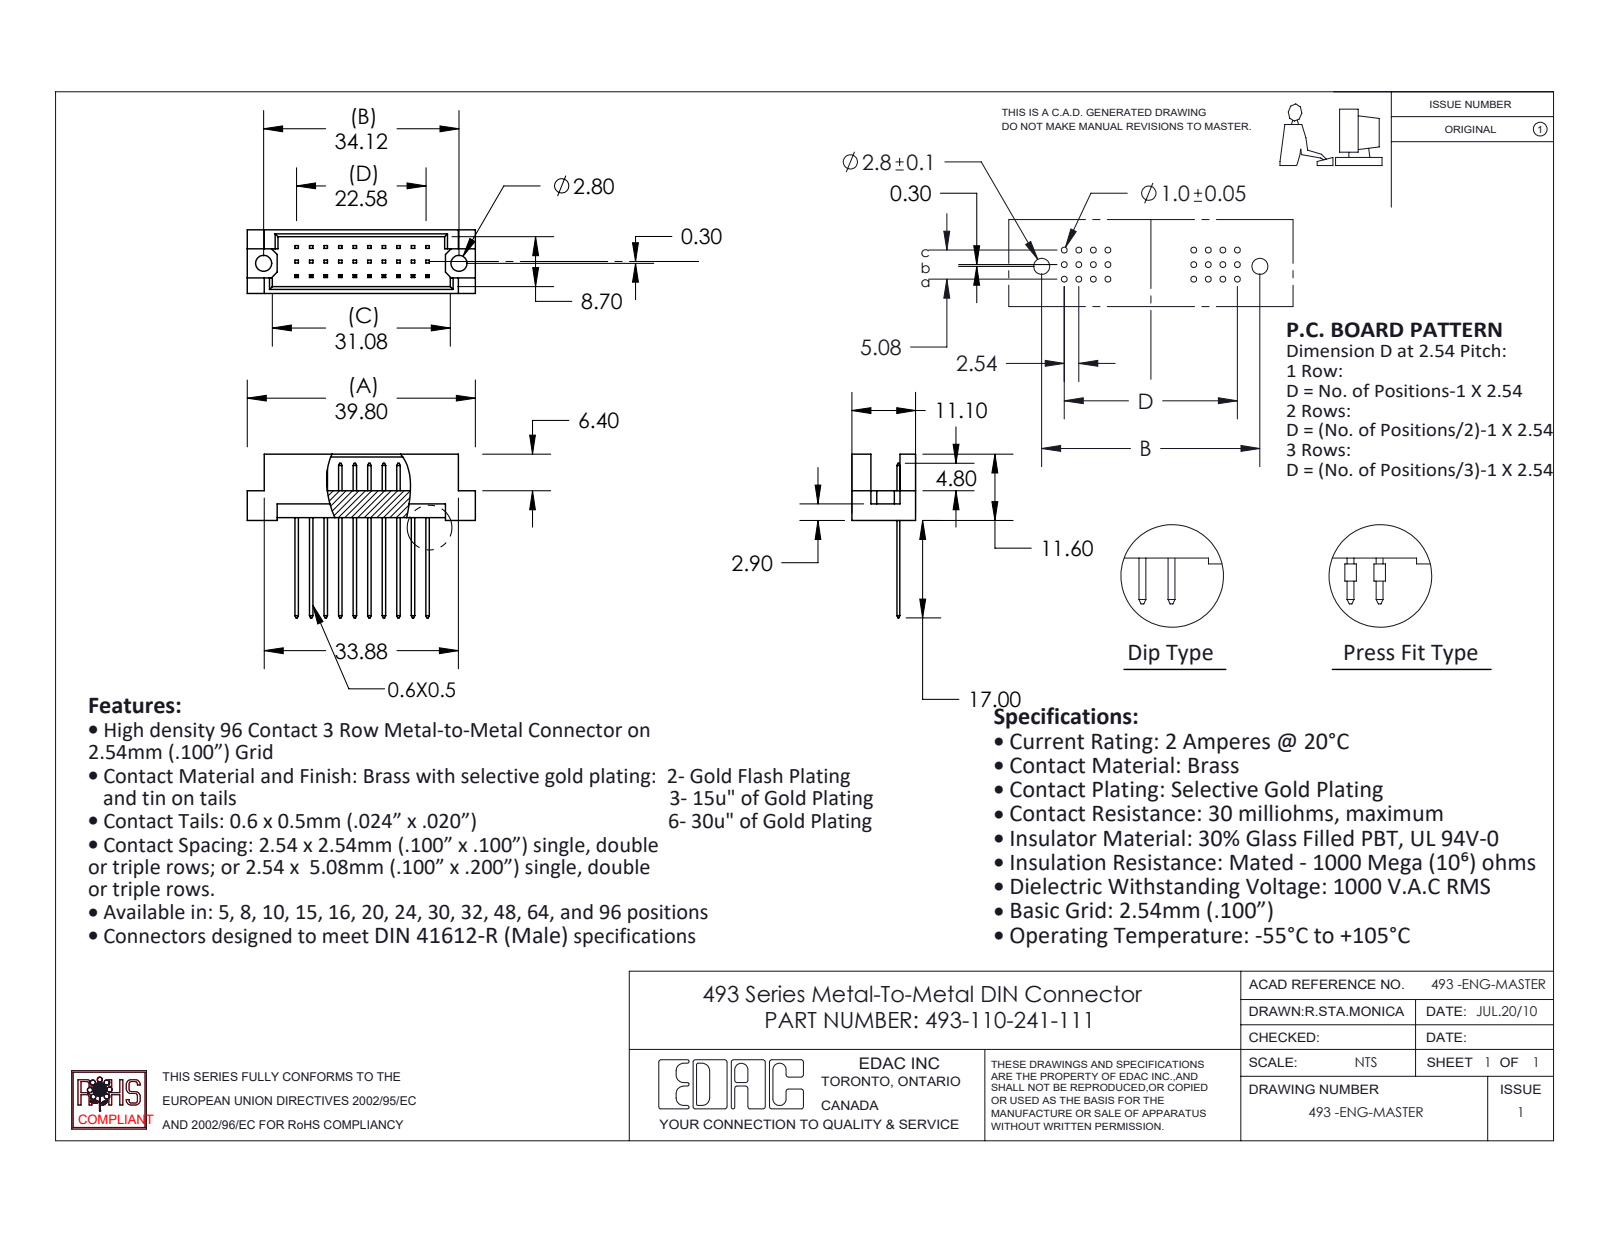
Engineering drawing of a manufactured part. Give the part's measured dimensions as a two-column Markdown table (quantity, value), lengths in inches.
| quantity | value |
| --- | --- |
| part name | 493-290_41; 493 Part_30; 493-110-241-112 |
| STEP written by | SolidWorks 2020 (CONFIG_CONTROL_DESIGN) |
| units | inches |
| bodies | 11 solids, 312 faces (308 planar, 4 cylindrical, 0 other) |
| overall size | 1.567 × 1.126 × 0.437 |
| volume | 0.15 in³ |
| surface area | 5.158 in² |
| round holes (diameter × count) | 0.11 × 2 |
| main face-to-face distances | 0.047, 0.39, 0.437, 0.1, 0.02, 0.2, 0.343, 0.185, 0.109, 0.128 |
| hole center spacings | 1.343 |
